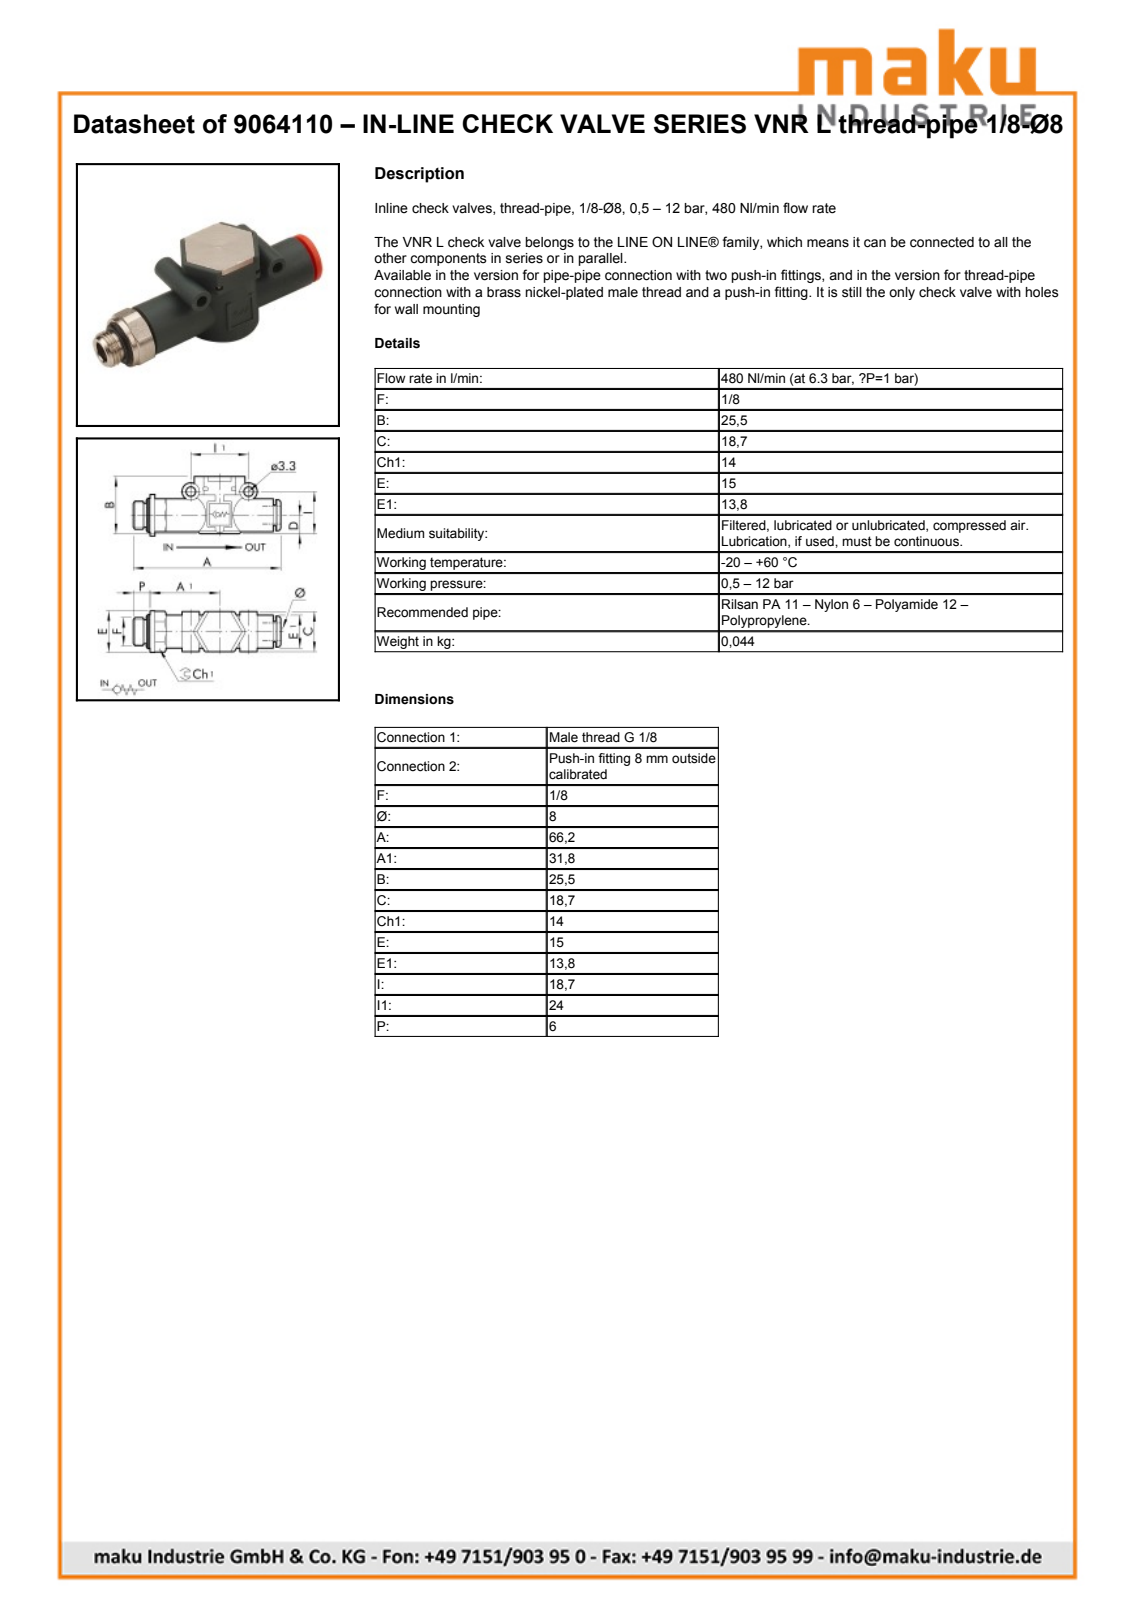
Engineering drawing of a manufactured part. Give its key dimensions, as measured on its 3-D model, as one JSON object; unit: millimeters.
{"part_name": "9064110; LINE-ON-LINE D8 VSR-L body; LINE-ON-LINE D8 VNR-L bushing; LINE-ON-LINE D8-1/8 thread port (+1 more)", "step_written_by": "PARTsolutions (AUTOMOTIVE_DESIGN)", "units": "millimeters", "bodies": {"solids": 4, "faces": 159, "planar": 97, "cylindrical": 51, "other": 11}, "overall_size": [66.4, 26, 18.7], "volume_mm3": 8632, "surface_area_mm2": 9554, "round_holes": [[3.3, 2], [6, 2], [5, 1], [5.5, 1], [8.1, 1], [9.4, 1], [11, 1], [11.66, 1], [12.5, 1], [15, 1]], "round_bosses_or_shafts": [[6, 2], [18.8, 1], [15, 1], [13.8, 1], [13.6, 1], [9.73, 1], [9.5, 1], [9.2, 1]], "partial_cylinders_radius": [[3.75, 1], [7.75, 1], [10.2, 1], [10.35, 1], [11.45, 1]], "face_to_face_distances": [1.9, 24.1, 26, 4.1, 20, 21.9, 0.94, 13.8, 36.2, 49.06], "hole_center_spacings": [15.37, 24]}
